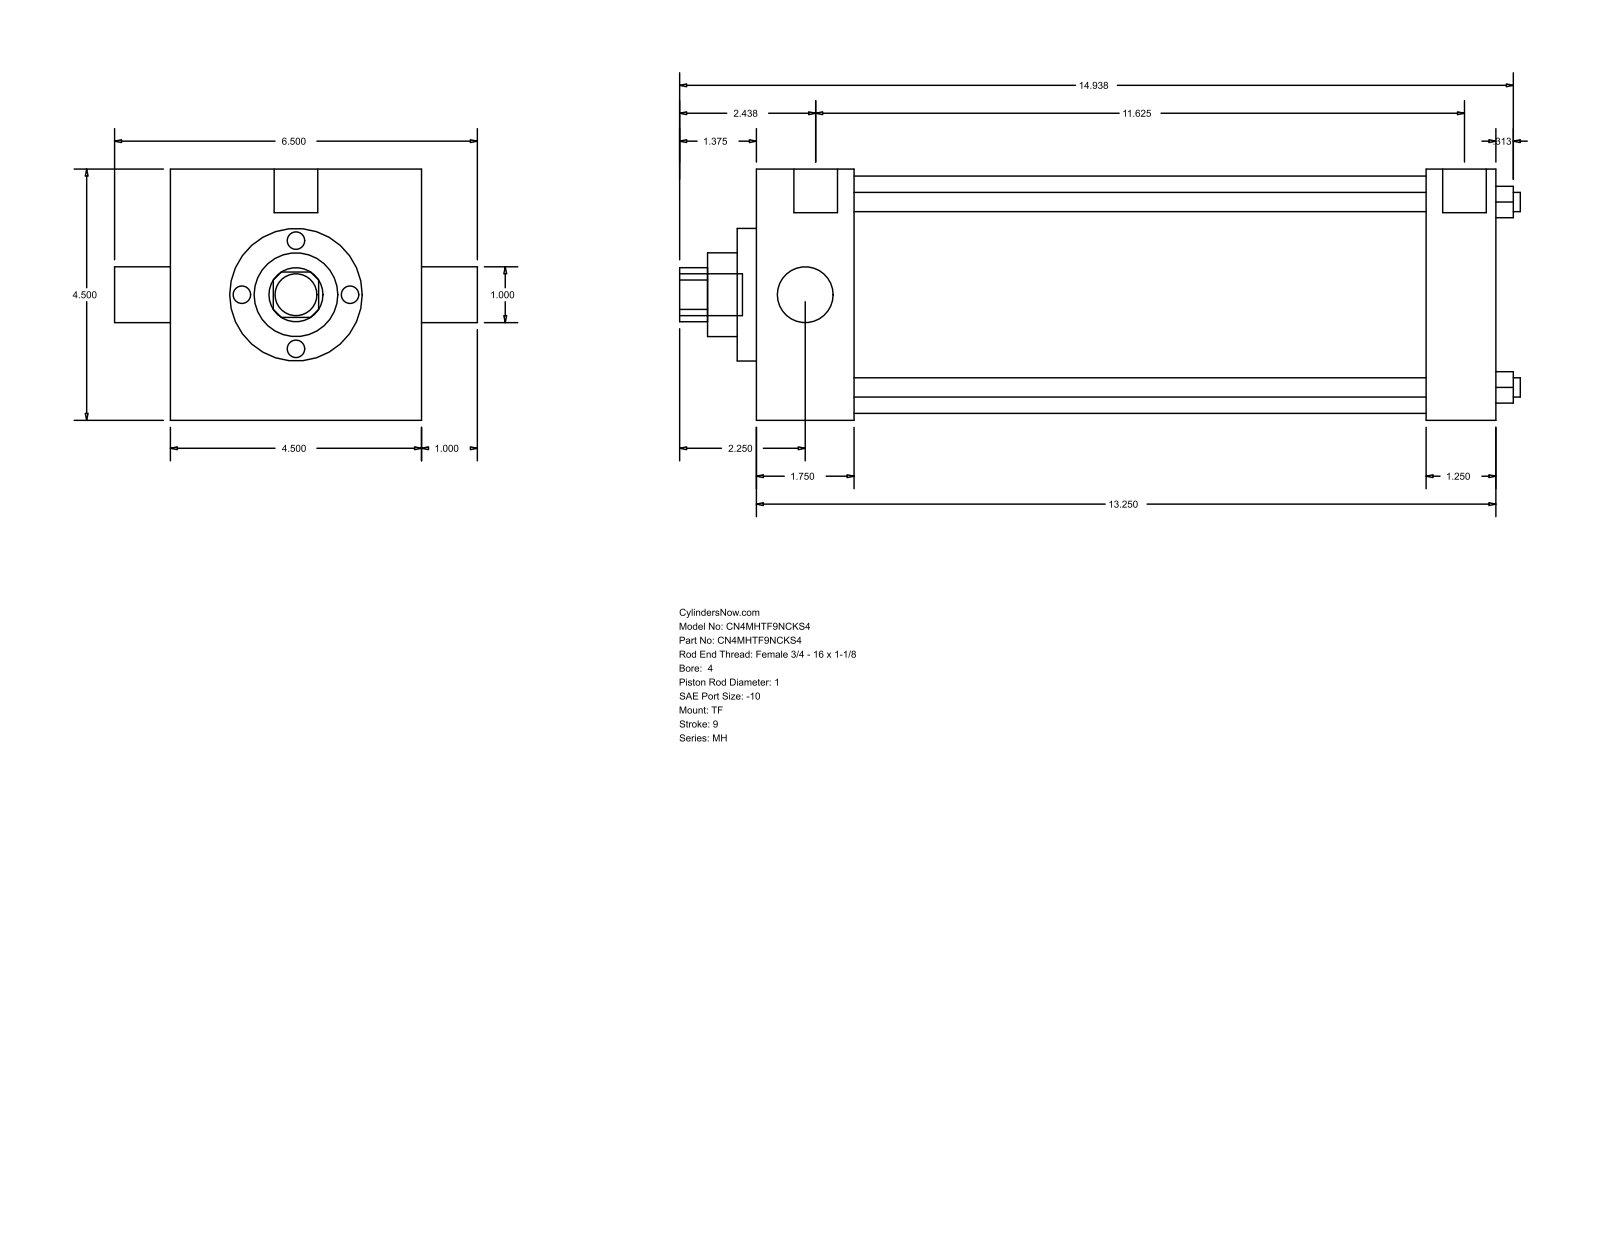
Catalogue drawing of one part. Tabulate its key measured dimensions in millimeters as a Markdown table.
| quantity | value |
| --- | --- |
| part name | MH_TF__0400_1 |
| STEP written by | GSSL Pune (CONFIG_CONTROL_DESIGN) |
| units | millimeters |
| bodies | 0 solids, 86 faces (61 planar, 25 cylindrical, 0 other) |
| overall size | 382.59 × 165.1 × 114.3 |
| round holes (diameter × count) | 8.76 × 4, 25.4 × 2, 38.1 × 1, 60.33 × 1, 107.95 × 1 |
| round bosses / shafts (diameter × count) | 8.73 × 3, 19.84 × 2, 19.05 × 1 |
| partial cylindrical surfaces (radius × count) | 12.29 × 1 |
| main face-to-face distances | 114.3, 336.56, 44.46, 292.1, 304.81, 260.35, 31.75, 8.73, 53.19, 313.54 |
| hole center spacings | 59.62, 84.32, 119.25 |
